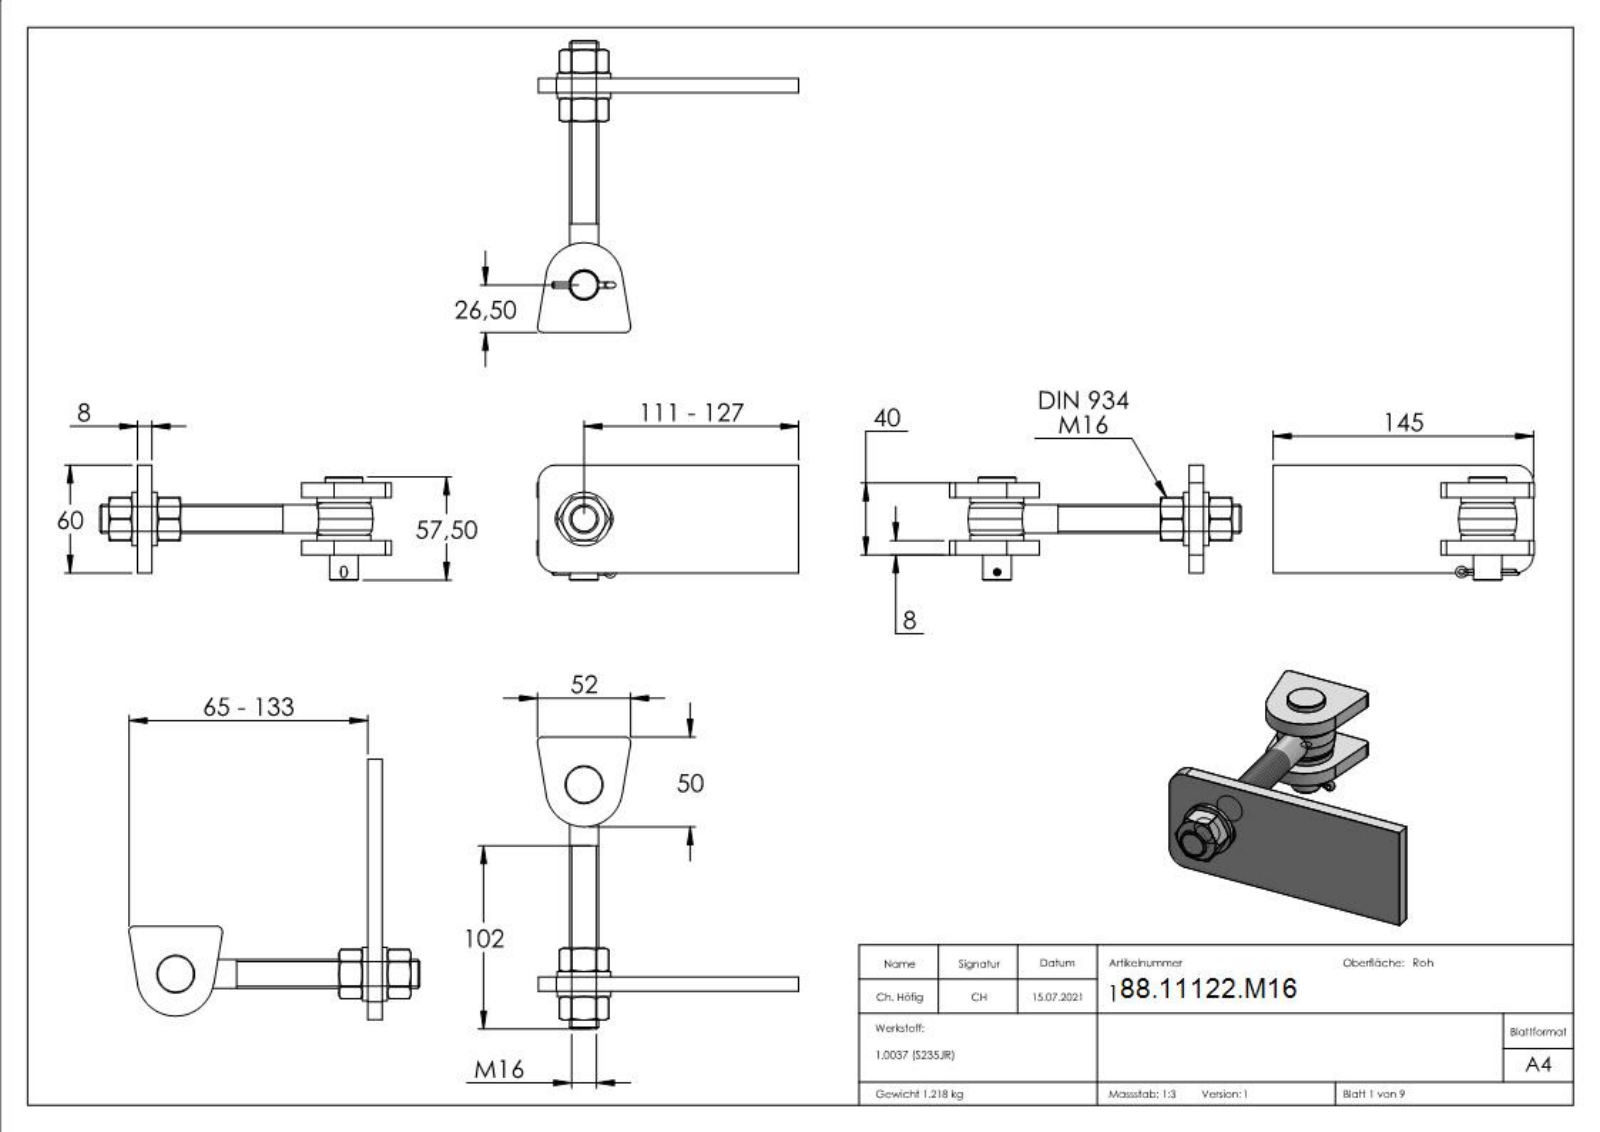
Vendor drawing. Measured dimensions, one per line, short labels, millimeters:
name: Torband Teil4_122-M16 Teil4; Torband Teil1_122-M16 Teil1; Splint DIN94 - ISO 1234 Konfig_DIN 94 3,2x30; 122-M16 (+4 more)
written by: SolidWorks 2018 (CONFIG_CONTROL_DESIGN)
unit: mm
bodies: 12 solids, 373 faces (176 planar, 66 cylindrical, 131 other)
size: 162.5 × 145.5 × 64.1
volume: 155 967 mm³; area: 55 379 mm²
holes: 2× ⌀17, 1× ⌀4, 1× ⌀14, 1× ⌀16.4, 1× ⌀16.8
bosses: 2× ⌀29.8, 1× ⌀21, 1× ⌀16, 1× ⌀15.9, 1× ⌀3.2
rounds: 6× R0.5, 2× R1, 2× R2.59, 2× R3, 2× R9, 2× R10, 1× R1.61, 1× R8.3
face distances: 8, 32, 24, 21, 11, 3, 18, 10, 42, 50
